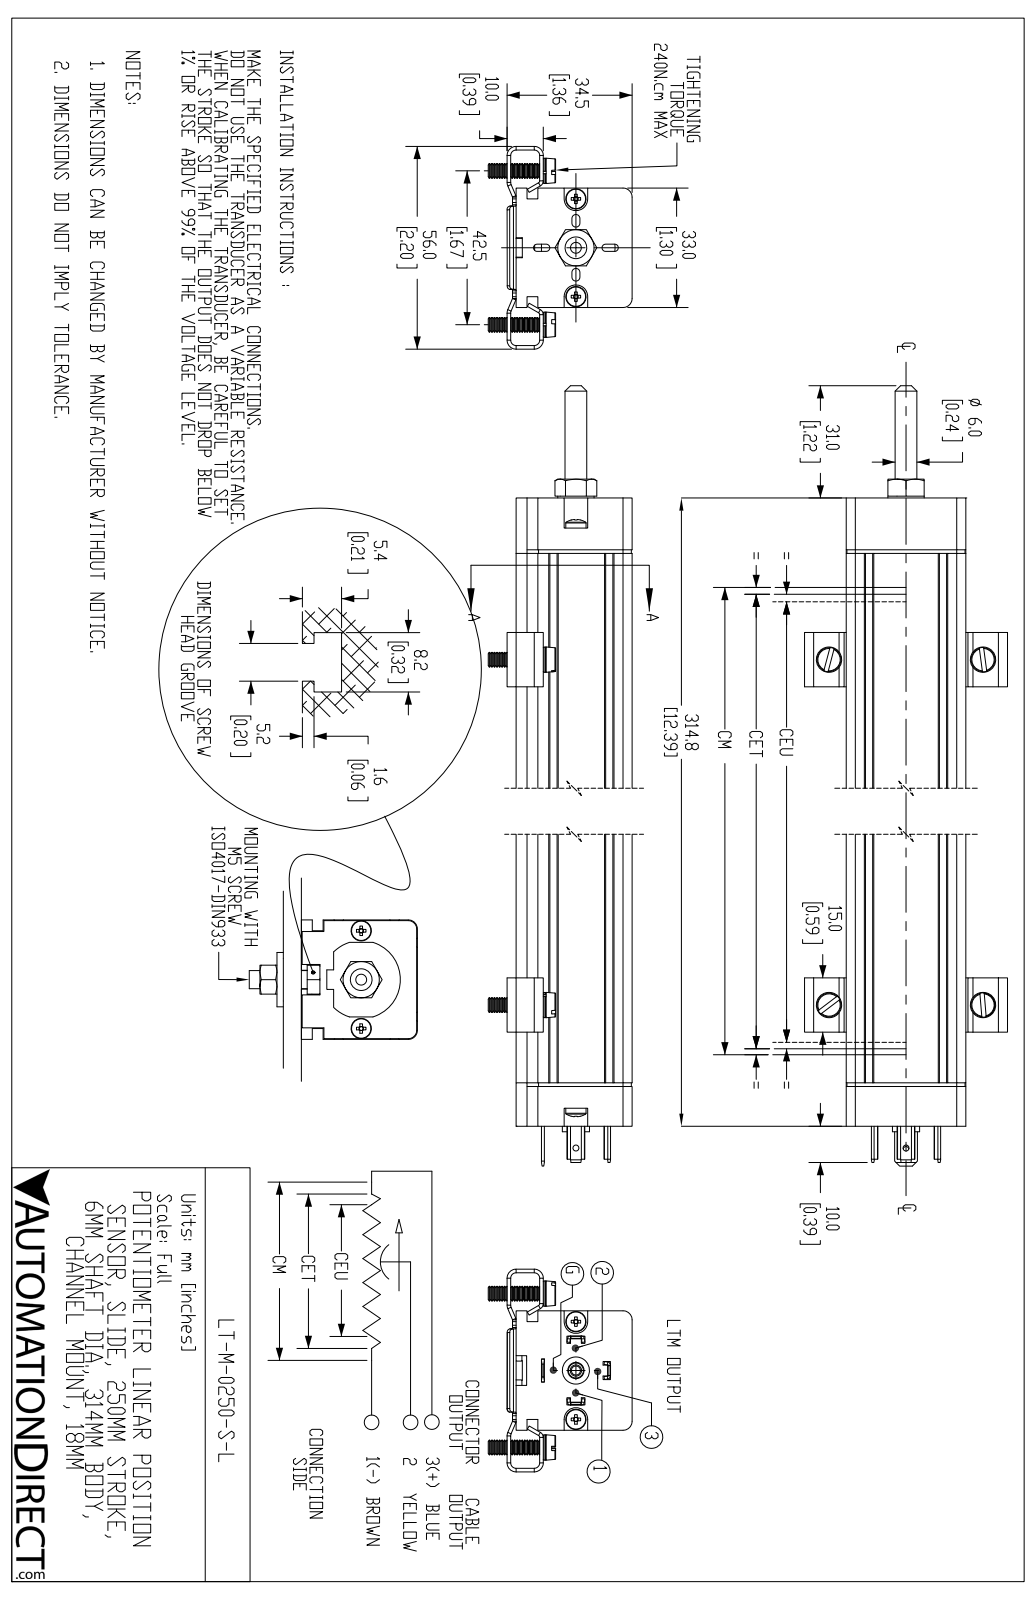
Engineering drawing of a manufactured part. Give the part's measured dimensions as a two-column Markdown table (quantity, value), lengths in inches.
| quantity | value |
| --- | --- |
| part name | LT-M-0250-S-L |
| STEP written by | SolidWorks 2019 (AUTOMOTIVE_DESIGN) |
| units | inches |
| bodies | 21 solids, 1620 faces (696 planar, 356 cylindrical, 568 other) |
| overall size | 14.741 × 2.205 × 1.563 |
| volume | 19.55 in³ |
| surface area | 118.9 in² |
| round holes (diameter × count) | 0.142 × 4, 0.059 × 2, 0.065 × 2, 0.108 × 2, 0.134 × 2, 0.169 × 2, 0.063 × 1, 0.098 × 1, 0.118 × 1, 0.163 × 1, 0.197 × 1, 0.276 × 1 |
| round bosses / shafts (diameter × count) | 0.274 × 4, 0.157 × 4, 0.22 × 2, 0.118 × 2, 0.295 × 1, 0.236 × 1, 0.177 × 1, 0.173 × 1 |
| partial cylindrical surfaces (radius × count) | 0.039 × 34, 0.098 × 12, 0.059 × 10, 0.085 × 8, 0.033 × 6, 0.043 × 4, 0.024 × 2, 0.063 × 2 |
| main face-to-face distances | 1.26, 1.299, 0.118, 0.039, 1.287, 0.213, 1.047, 0.488, 0.799, 0.811 |
| hole center spacings | 0.484, 0.531, 1.359, 1.663, 1.673, 1.766, 1.78, 9.756 |
